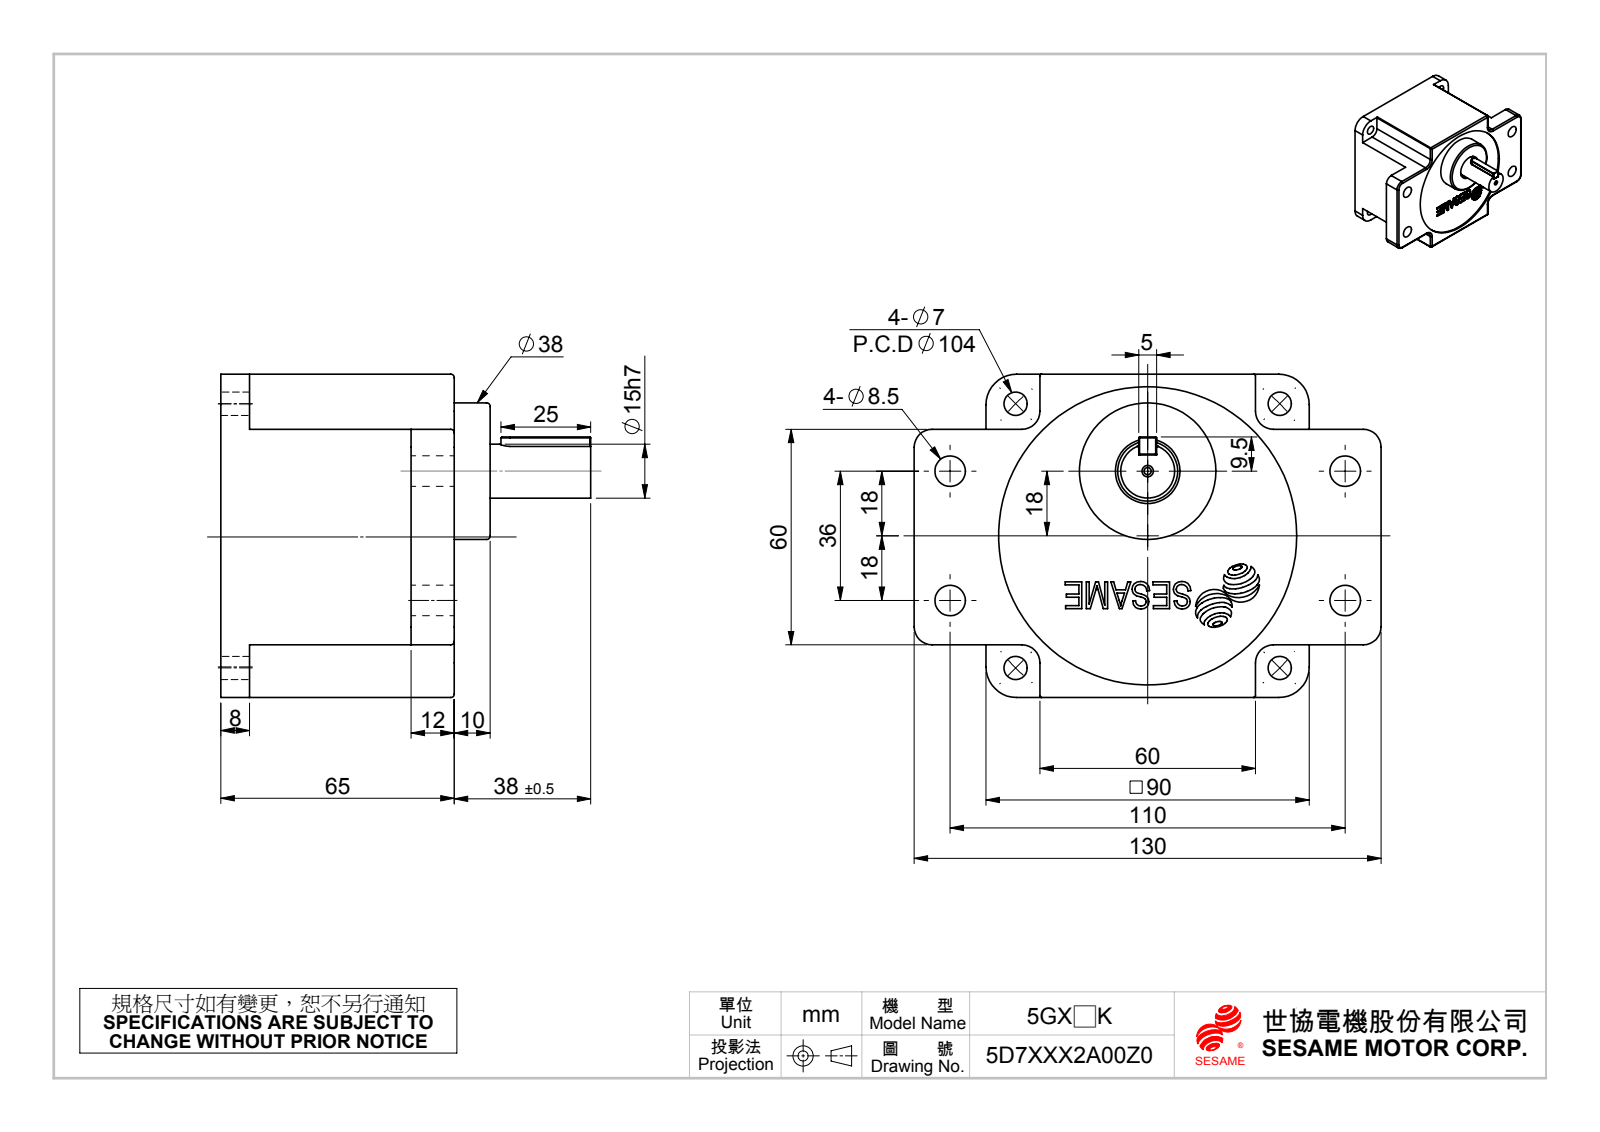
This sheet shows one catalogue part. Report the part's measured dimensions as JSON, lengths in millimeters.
{"part_name": "側板成品(簡易); 1715-2A_5.成品; 5x5xL_25L; G583-U·s", "step_written_by": "SolidWorks 2010 (CONFIG_CONTROL_DESIGN)", "units": "millimeters", "bodies": {"solids": 4, "faces": 509, "planar": 152, "cylindrical": 246, "other": 111}, "overall_size": [130, 103, 90], "volume_mm3": 481822, "surface_area_mm2": 68138, "round_holes": [[3.3, 4], [6.5, 4], [8.5, 4], [4, 2], [2, 1], [12.2, 1], [18, 1], [82.97, 1], [83, 1], [85.77, 1]], "round_bosses_or_shafts": [[82.8, 1], [70, 1], [38, 1], [16.7, 1], [15, 1]], "partial_cylinders_radius": [[1, 22], [0.5, 16], [0.95, 8], [1.82, 8], [2.02, 8], [3.55, 8], [5, 8], [0.25, 4]], "face_to_face_distances": [90, 56, 1, 55, 5.6, 60.6, 61.6, 75, 60, 9], "hole_center_spacings": [26.17, 52, 57.72, 57.87, 63.53, 73.54, 93.67, 106.87]}
